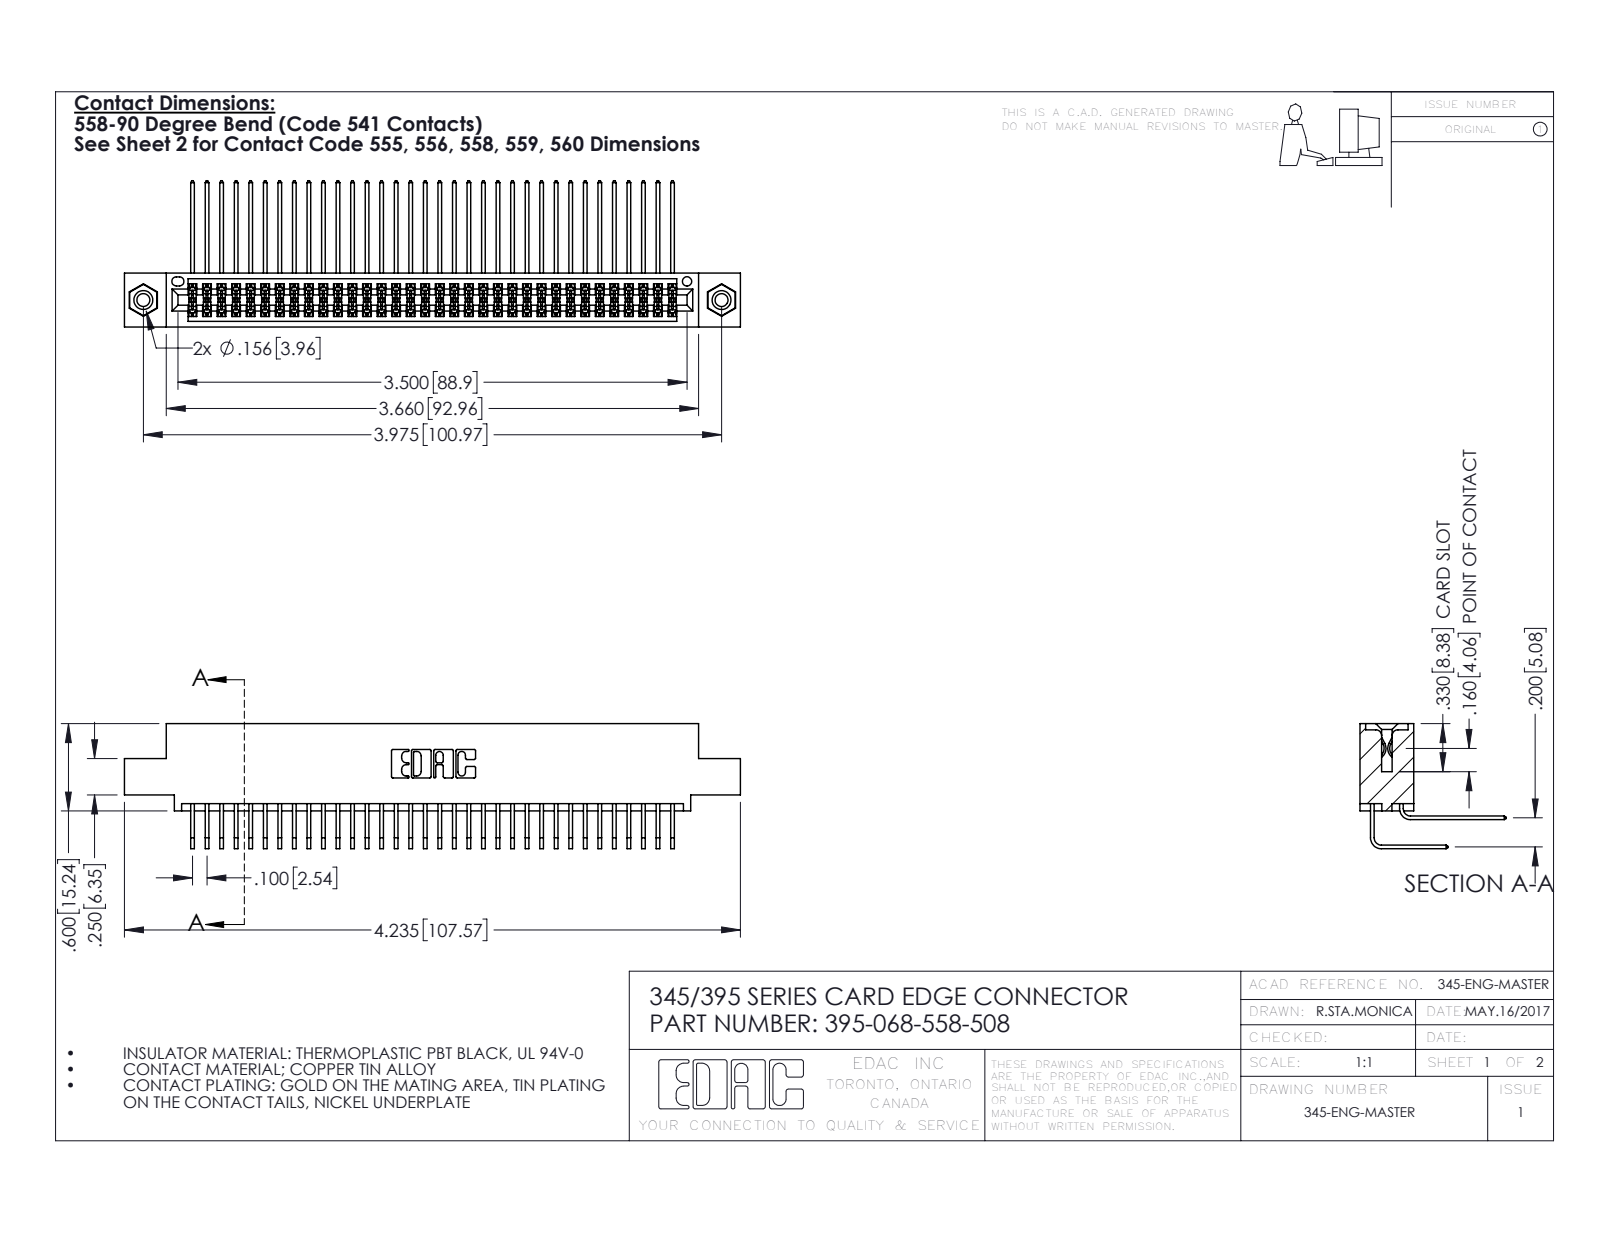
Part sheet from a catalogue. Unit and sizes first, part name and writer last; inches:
Units: inches
Overall size (bounding box): 4.235 × 1.005 × 0.859
Round holes (diameter × count): ⌀0.089 ×2, ⌀0.125 ×2, ⌀0.156 ×2, ⌀0.064 ×1
Round bosses / shafts (diameter × count): ⌀0.155 ×2
Partial cylindrical surfaces — rounded edges, fillets, slot ends (radius × count): R0.006 ×103, R0.01 ×22, R0.007 ×6, R0.031 ×6, R0.026 ×3, R0.014 ×2, R0.019 ×2, R0.022 ×2
Main face-to-face distances: 0.072, 0.298, 0.2, 0.37, 0.098, 0.272, 0.025, 0.225, 0.025, 0.175
Hole centre spacings: 0.27, 3.74, 3.975
Volume: 0.652 in³ · Surface area: 27.27 in²
Bodies: 71 solids, 3726 faces (2496 planar, 1214 cylindrical, 16 other)
Part name (STEP PRODUCT): 345-292-001_558 559 Tail - 1; 345 Part_0.110 Offset - 0.156 Dia-TI; 395-068-558-508; 345-292-001_558 Tail - 2 (+1 more)
STEP written by: SolidWorks 2016 (CONFIG_CONTROL_DESIGN)
